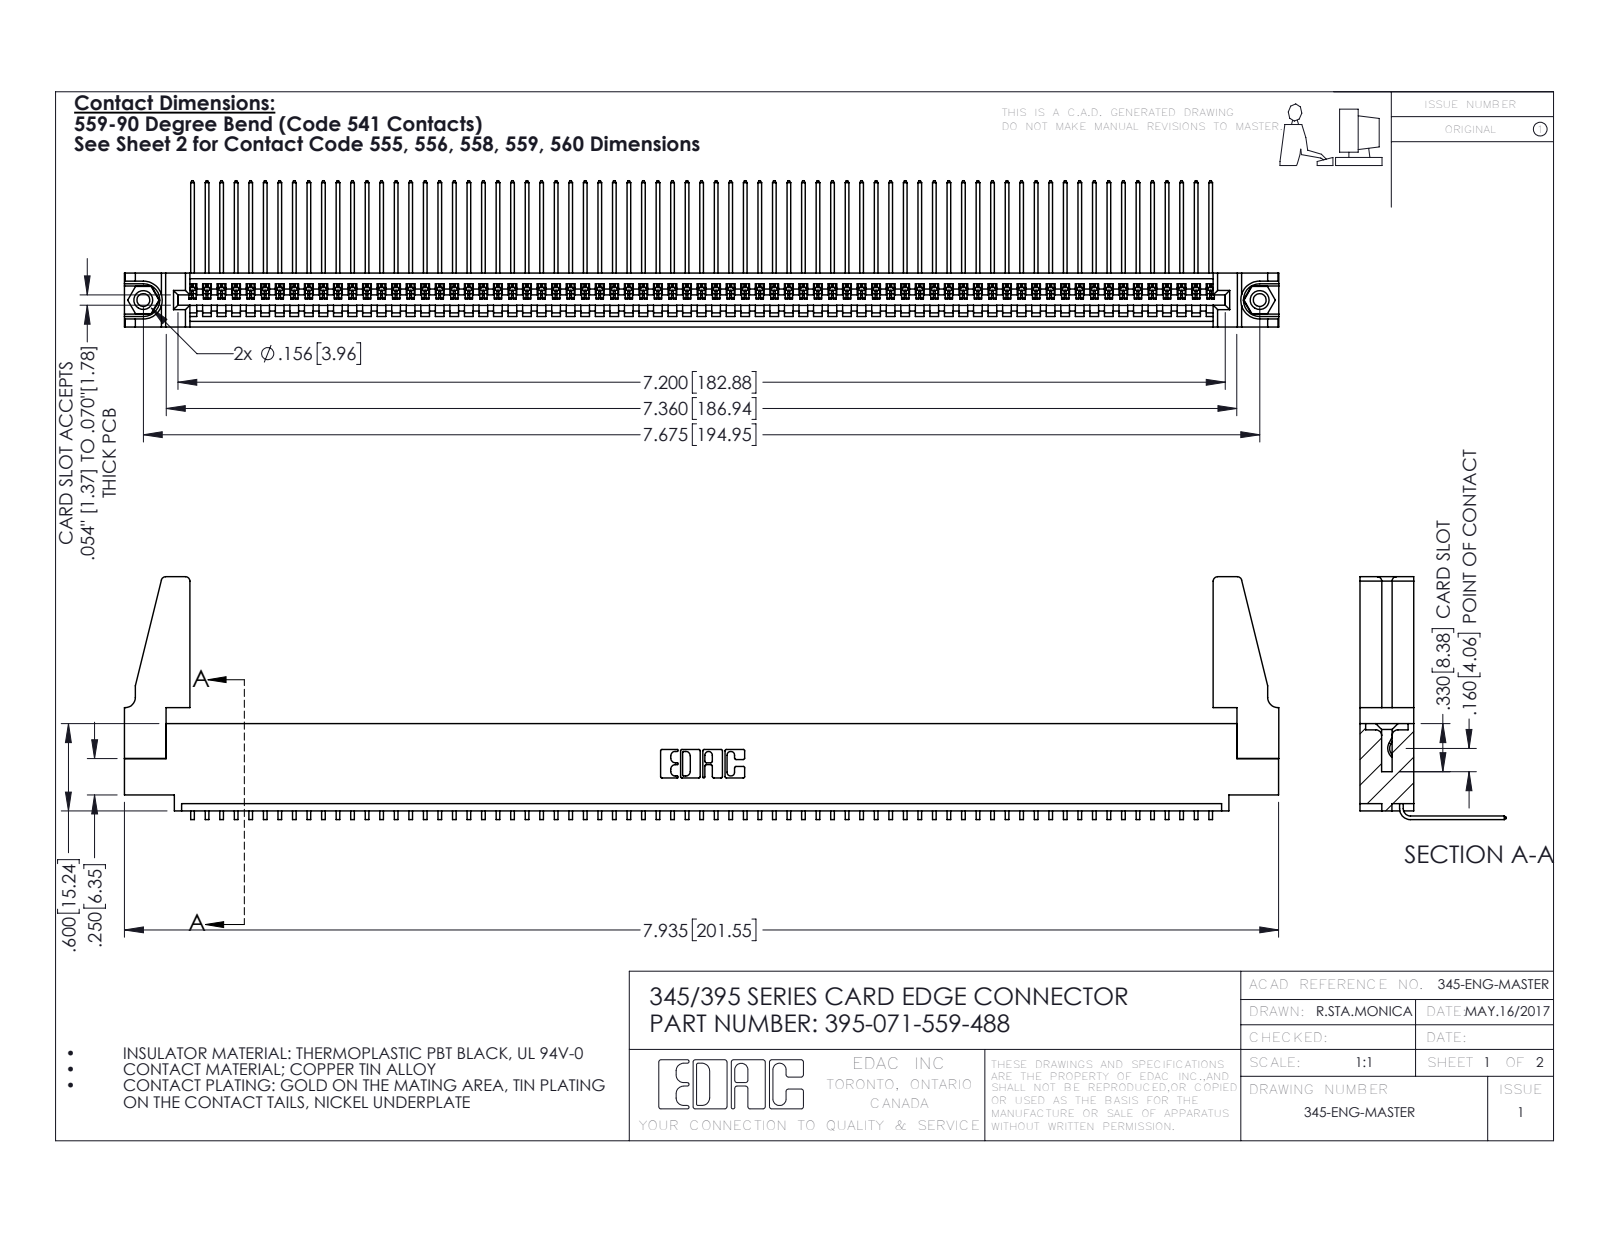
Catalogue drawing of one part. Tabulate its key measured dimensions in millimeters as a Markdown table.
| quantity | value |
| --- | --- |
| part name | 345-220-078_345-220-088; 395-071-559-488; 345-292-001_558 559 Tail - 1; 345-250-001_345-250-001-102 (+1 more) |
| STEP written by | SolidWorks 2016 (CONFIG_CONTROL_DESIGN) |
| units | millimeters |
| bodies | 76 solids, 4514 faces (3138 planar, 1360 cylindrical, 16 other) |
| overall size | 201.6 × 42.4 × 25.5 |
| volume | 22 790 mm³ |
| surface area | 30 970 mm² |
| round holes (diameter × count) | 2.3 × 2, 3.2 × 2, 4 × 2, 1.6 × 1 |
| round bosses / shafts (diameter × count) | 3.9 × 2 |
| partial cylindrical surfaces (radius × count) | 0.2 × 142, 0.3 × 22, 0.8 × 8, 0.2 × 6, 0.8 × 6, 0.7 × 3, 0.8 × 2, 1 × 2 |
| main face-to-face distances | 1.8, 7.6, 9.4, 2.5, 6.9, 0.6, 5.1, 5.7, 3.8, 1.8 |
| hole center spacings | 6.9, 189, 194.9 |
